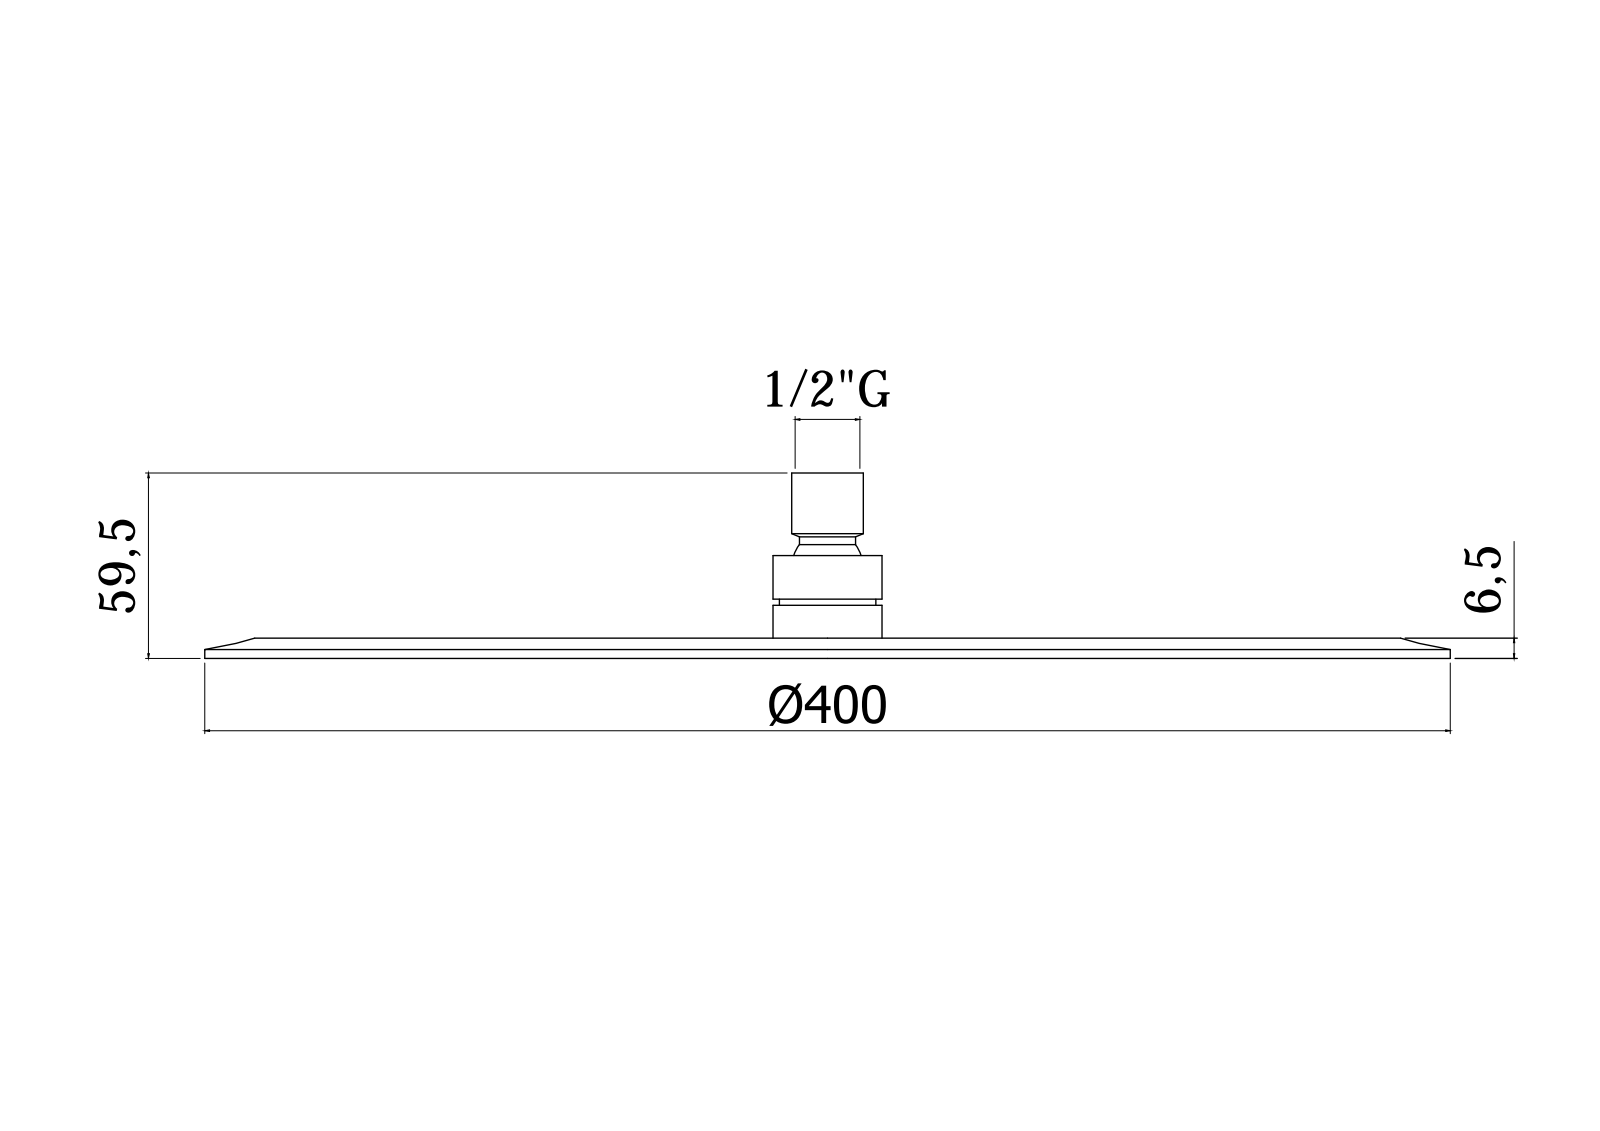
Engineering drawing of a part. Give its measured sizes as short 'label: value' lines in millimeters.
name: ZSOF103CR
written by: CREO PARAMETRIC BY PTC INC, 2020044 (CONFIG_CONTROL_DESIGN)
unit: mm
bodies: 1 solid, 4492 faces (647 planar, 1288 cylindrical, 2557 other)
size: 400 × 400 × 45.3
volume: 280 733 mm³; area: 509 924 mm²
holes: 126× ⌀1.5, 126× ⌀1.7, 1× ⌀7, 1× ⌀15, 1× ⌀16, 1× ⌀16.5, 1× ⌀18.63, 1× ⌀23.1, 1× ⌀23.8, 1× ⌀24
bosses: 126× ⌀10, 126× ⌀5, 1× ⌀400, 1× ⌀31.8, 1× ⌀28, 1× ⌀23.2, 1× ⌀22.9
face distances: 1, 4, 3, 5, 2, 1.2, 2.2, 5.2, 6.2, 3.2
hole spacings: 175, 348.67, 119.71, 286.7, 317.21, 200.75, 247.49, 90.59
